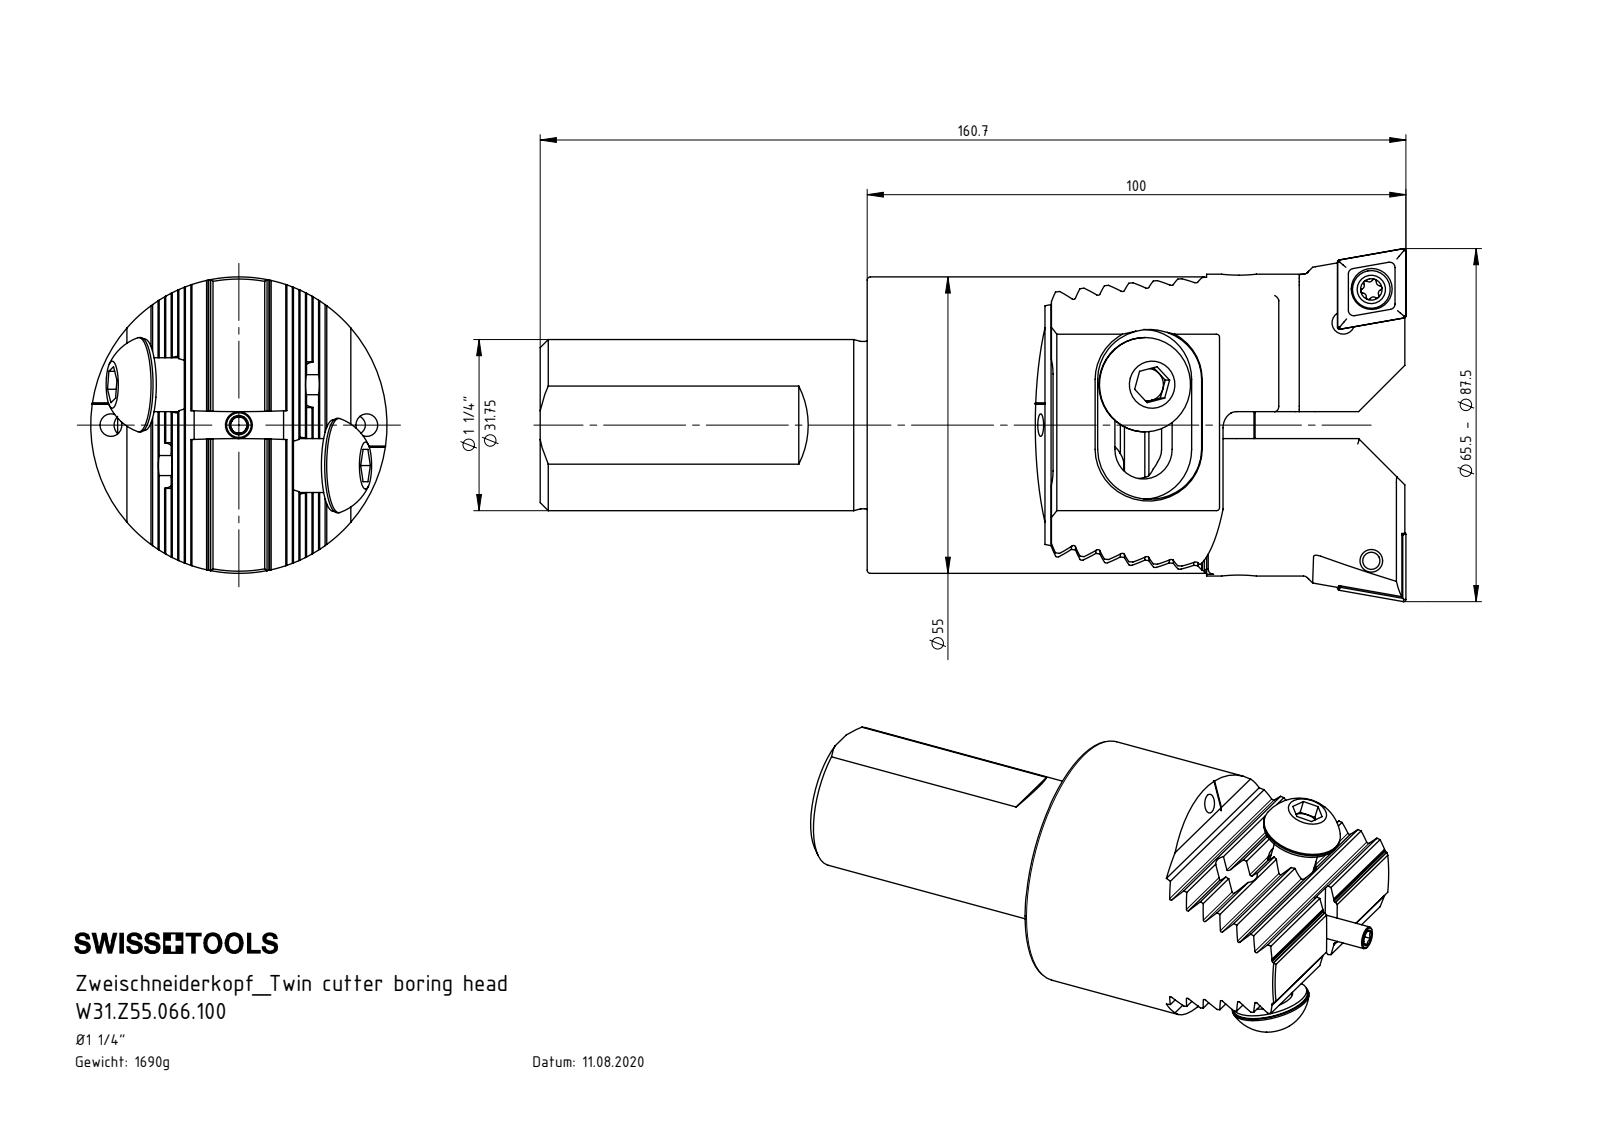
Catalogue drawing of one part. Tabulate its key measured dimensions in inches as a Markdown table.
| quantity | value |
| --- | --- |
| part name | W31.Z55.066.100; W31-Z55.K23.100_B; Z55-ER1.002.025_A; Z55-ER1.001.025 (+2 more) |
| STEP written by | SolidWorks 2022 (CONFIG_CONTROL_DESIGN) |
| units | inches |
| bodies | 6 solids, 308 faces (153 planar, 88 cylindrical, 67 other) |
| overall size | 5.224 × 2.165 × 2.165 |
| volume | 9.397 in³ |
| surface area | 47.17 in² |
| round holes (diameter × count) | 0.165 × 3, 0.335 × 2, 0.413 × 2, 0.433 × 2, 0.118 × 1, 0.13 × 1, 0.421 × 1, 0.531 × 1 |
| round bosses / shafts (diameter × count) | 0.689 × 2, 0.669 × 2, 0.394 × 2, 2.165 × 1, 1.25 × 1, 1.222 × 1, 0.197 × 1, 0.157 × 1 |
| partial cylindrical surfaces (radius × count) | 0.013 × 14, 8.661 × 2 |
| main face-to-face distances | 0.16, 0.32, 0.481, 0.641, 0.802, 0.641, 0.481, 0.321, 0.26, 2.48 |
